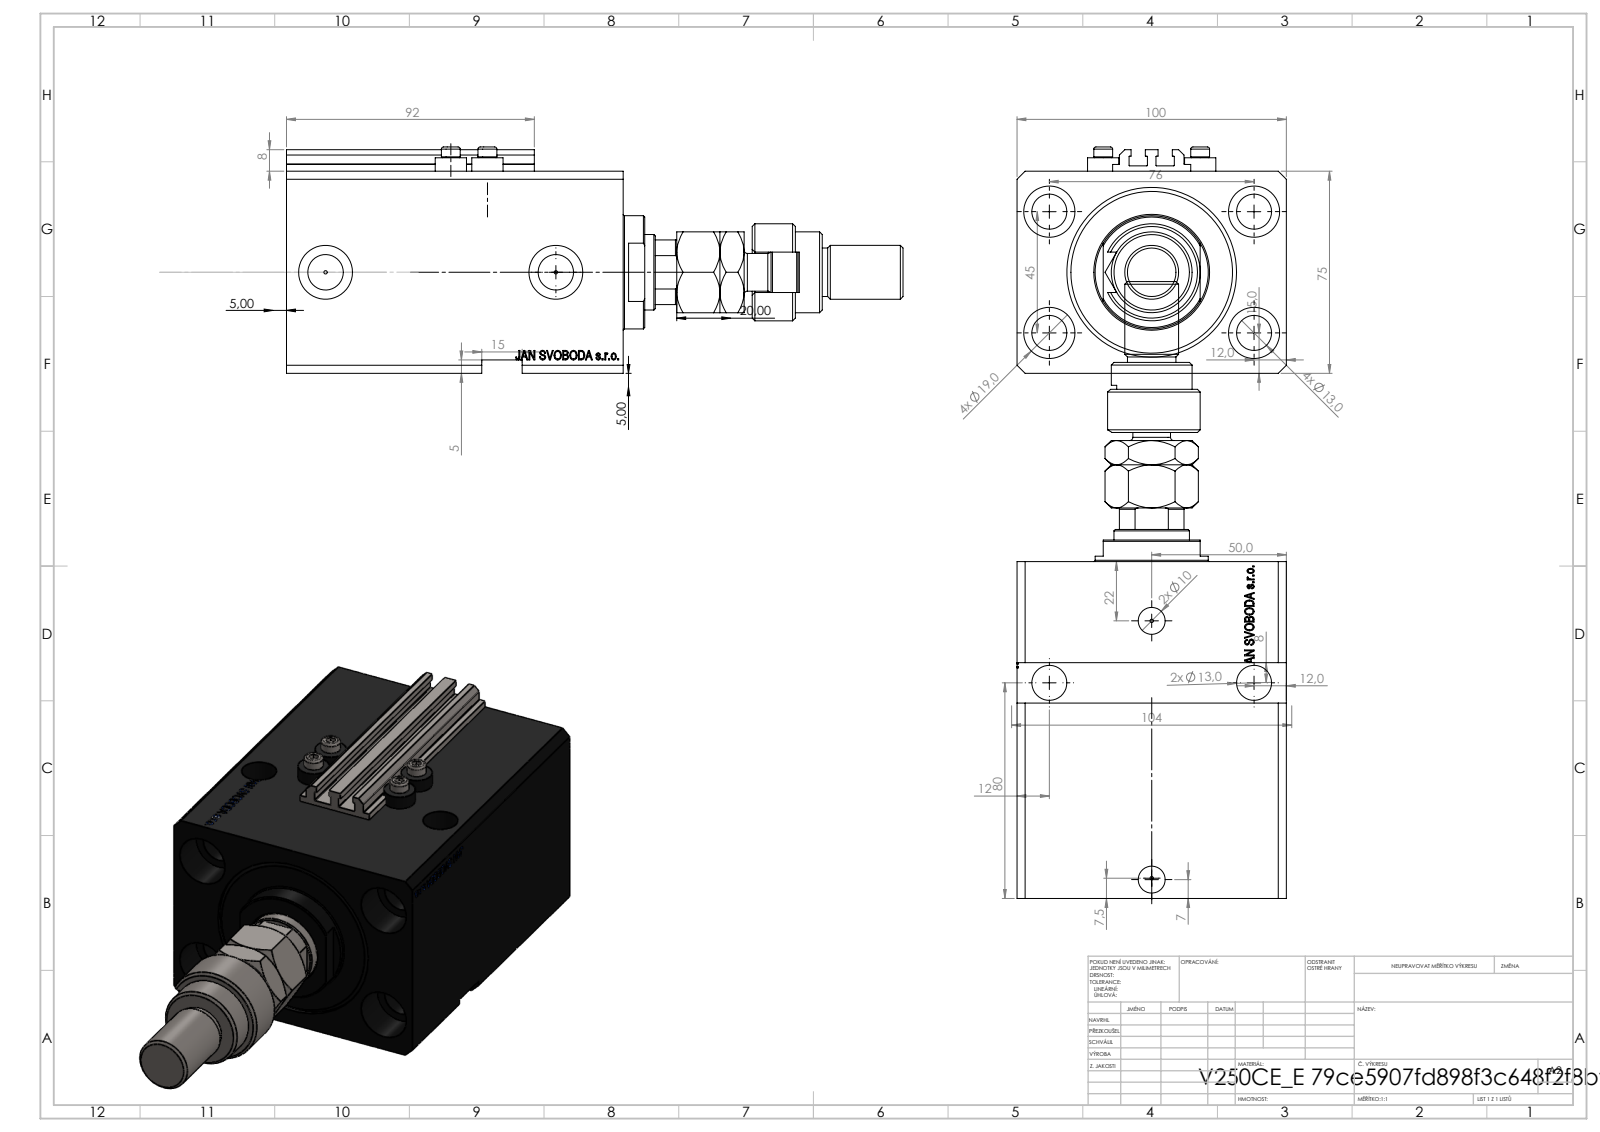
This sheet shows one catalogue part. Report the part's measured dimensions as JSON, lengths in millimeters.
{"part_name": "FEMALE_PART_FOR_DFA; V250CE_E_Body; V250CE_VC_E; V250CE_C_VCP (+2 more)", "step_written_by": "SolidWorks 2019 (CONFIG_CONTROL_DESIGN)", "units": "millimeters", "bodies": {"solids": 10, "faces": 1193, "planar": 563, "cylindrical": 159, "other": 471}, "overall_size": [229, 100, 84], "volume_mm3": 817731, "surface_area_mm2": 163592, "round_holes": [[13, 8], [1.25, 4], [4, 4], [19, 4], [10, 2], [13.16, 2], [20, 2], [18.5, 1], [28, 1], [50, 1], [63, 1]], "round_bosses_or_shafts": [[11.6, 4], [7, 4], [42, 1], [36, 1], [30, 1], [22, 1], [20, 1], [18, 1]], "partial_cylinders_radius": [[0.2, 10], [7.5, 1], [12, 1], [13.5, 1]], "face_to_face_distances": [75, 100, 20, 125, 11.9, 113.1, 105, 93.1, 70, 55], "hole_center_spacings": [44.16, 76, 13.6, 20.72, 27.59, 29, 33.62, 36]}
